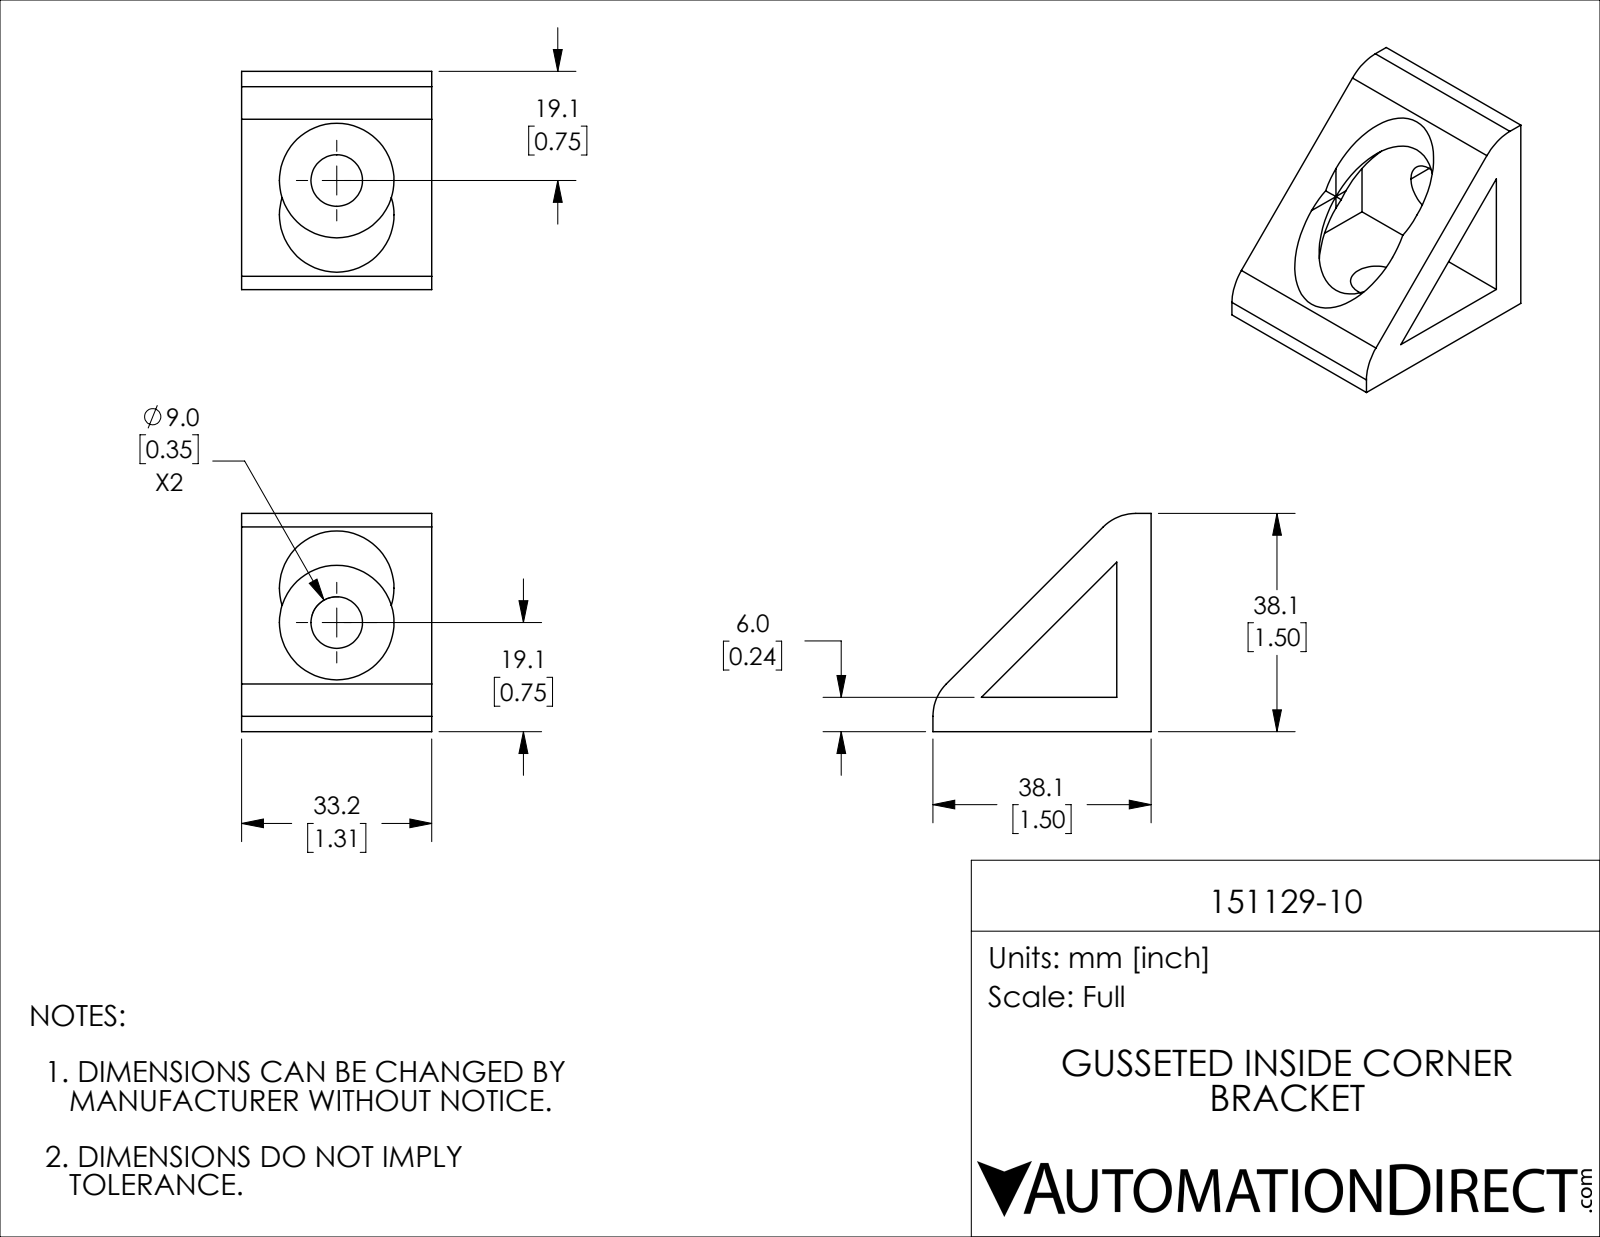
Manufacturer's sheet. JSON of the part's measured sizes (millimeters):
{"part_name": "151129-10", "step_written_by": "SolidWorks 2024 (CONFIG_CONTROL_DESIGN)", "units": "millimeters", "bodies": {"solids": 1, "faces": 28, "planar": 10, "cylindrical": 18, "other": 0}, "overall_size": [38.1, 38.1, 33.2], "volume_mm3": 17892, "surface_area_mm2": 7934, "round_holes": [[9, 2], [20, 2]], "partial_cylinders_radius": [[8, 2]], "face_to_face_distances": [6, 33.2, 38.1, 32.1]}
